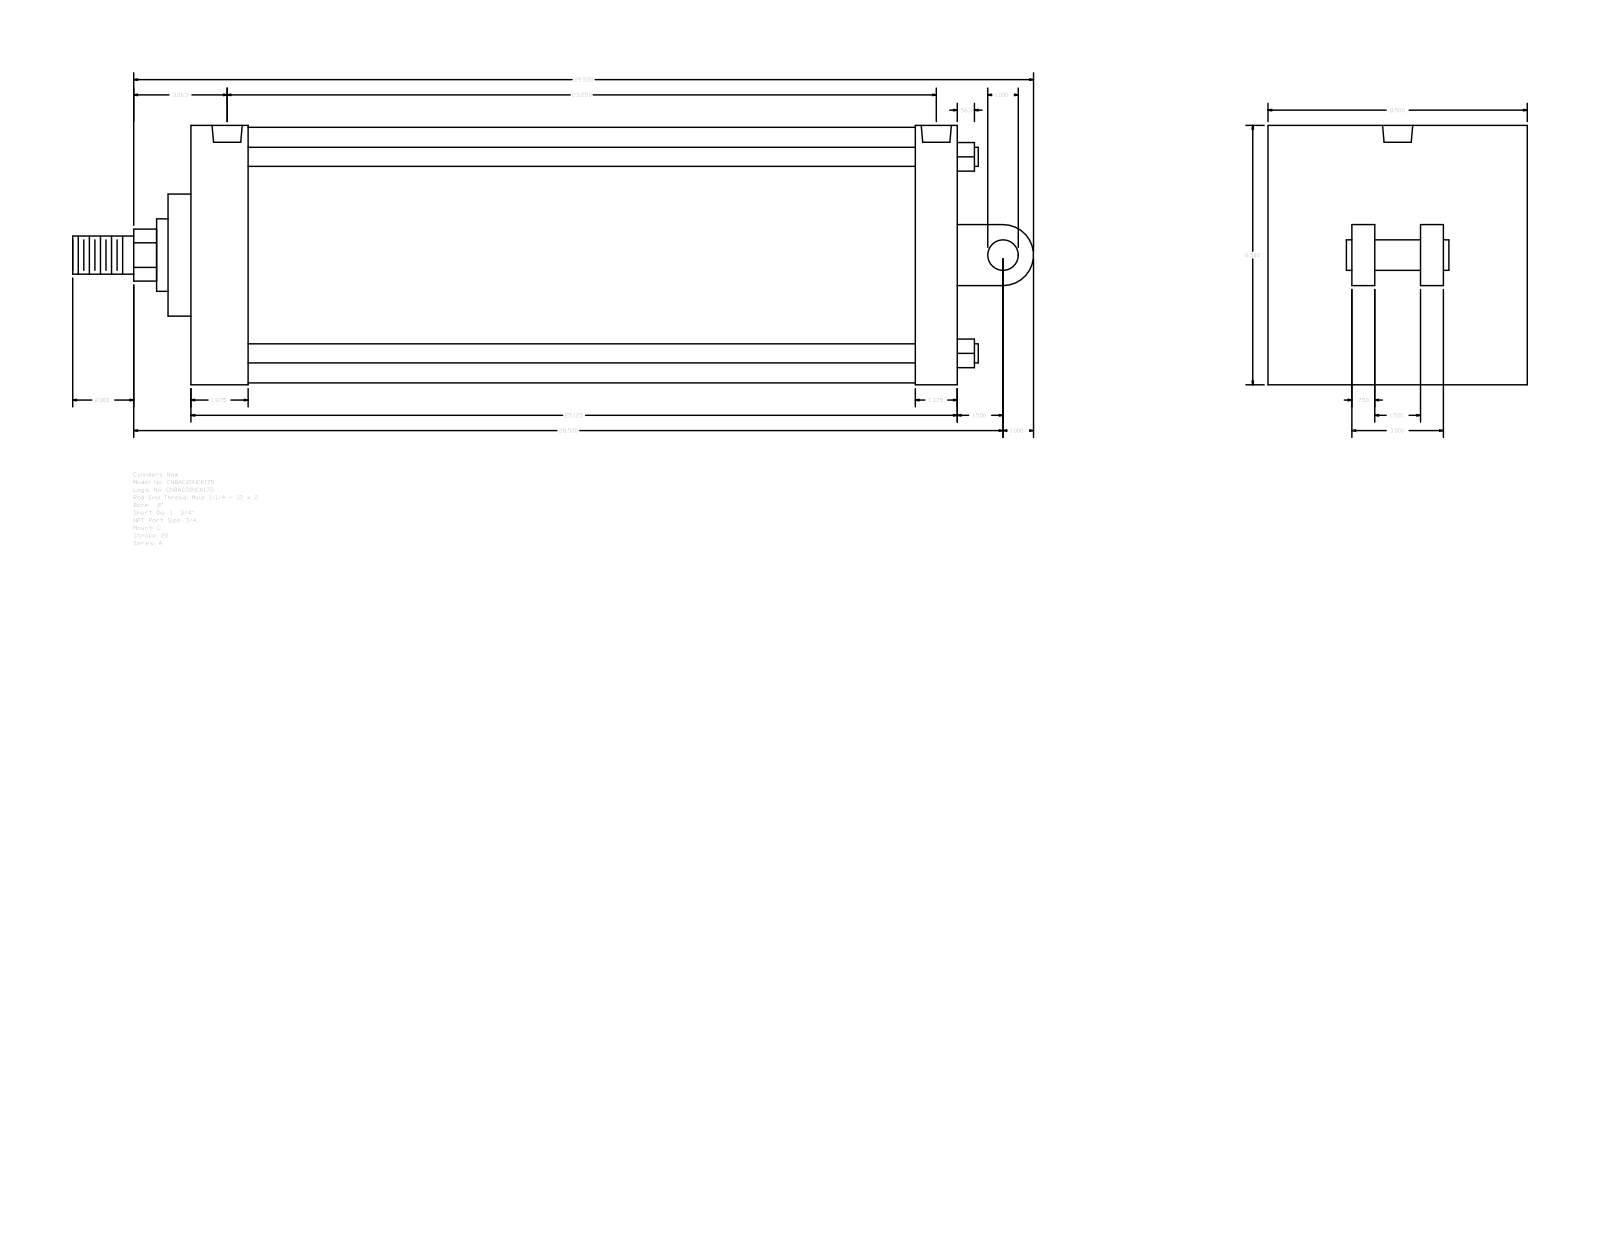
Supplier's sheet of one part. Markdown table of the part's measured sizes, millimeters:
| quantity | value |
| --- | --- |
| part name | A_C__0800_1.75 |
| STEP written by | GSSL Pune (CONFIG_CONTROL_DESIGN) |
| units | millimeters |
| bodies | 0 solids, 104 faces (75 planar, 29 cylindrical, 0 other) |
| overall size | 800.1 × 215.9 × 215.9 |
| round holes (diameter × count) | 15.08 × 4, 25.12 × 2 |
| round bosses / shafts (diameter × count) | 15.88 × 4, 212.72 × 1, 60.33 × 1, 44.45 × 1, 31.75 × 1, 25.4 × 1 |
| partial cylindrical surfaces (radius × count) | 21.63 × 1, 25.4 × 1 |
| main face-to-face distances | 638.18, 215.9, 19.05, 57.15, 47.63, 590.55, 603.26, 555.63, 34.92, 69.85 |
| hole center spacings | 6.35, 577.85, 584.2, 590.55 |
